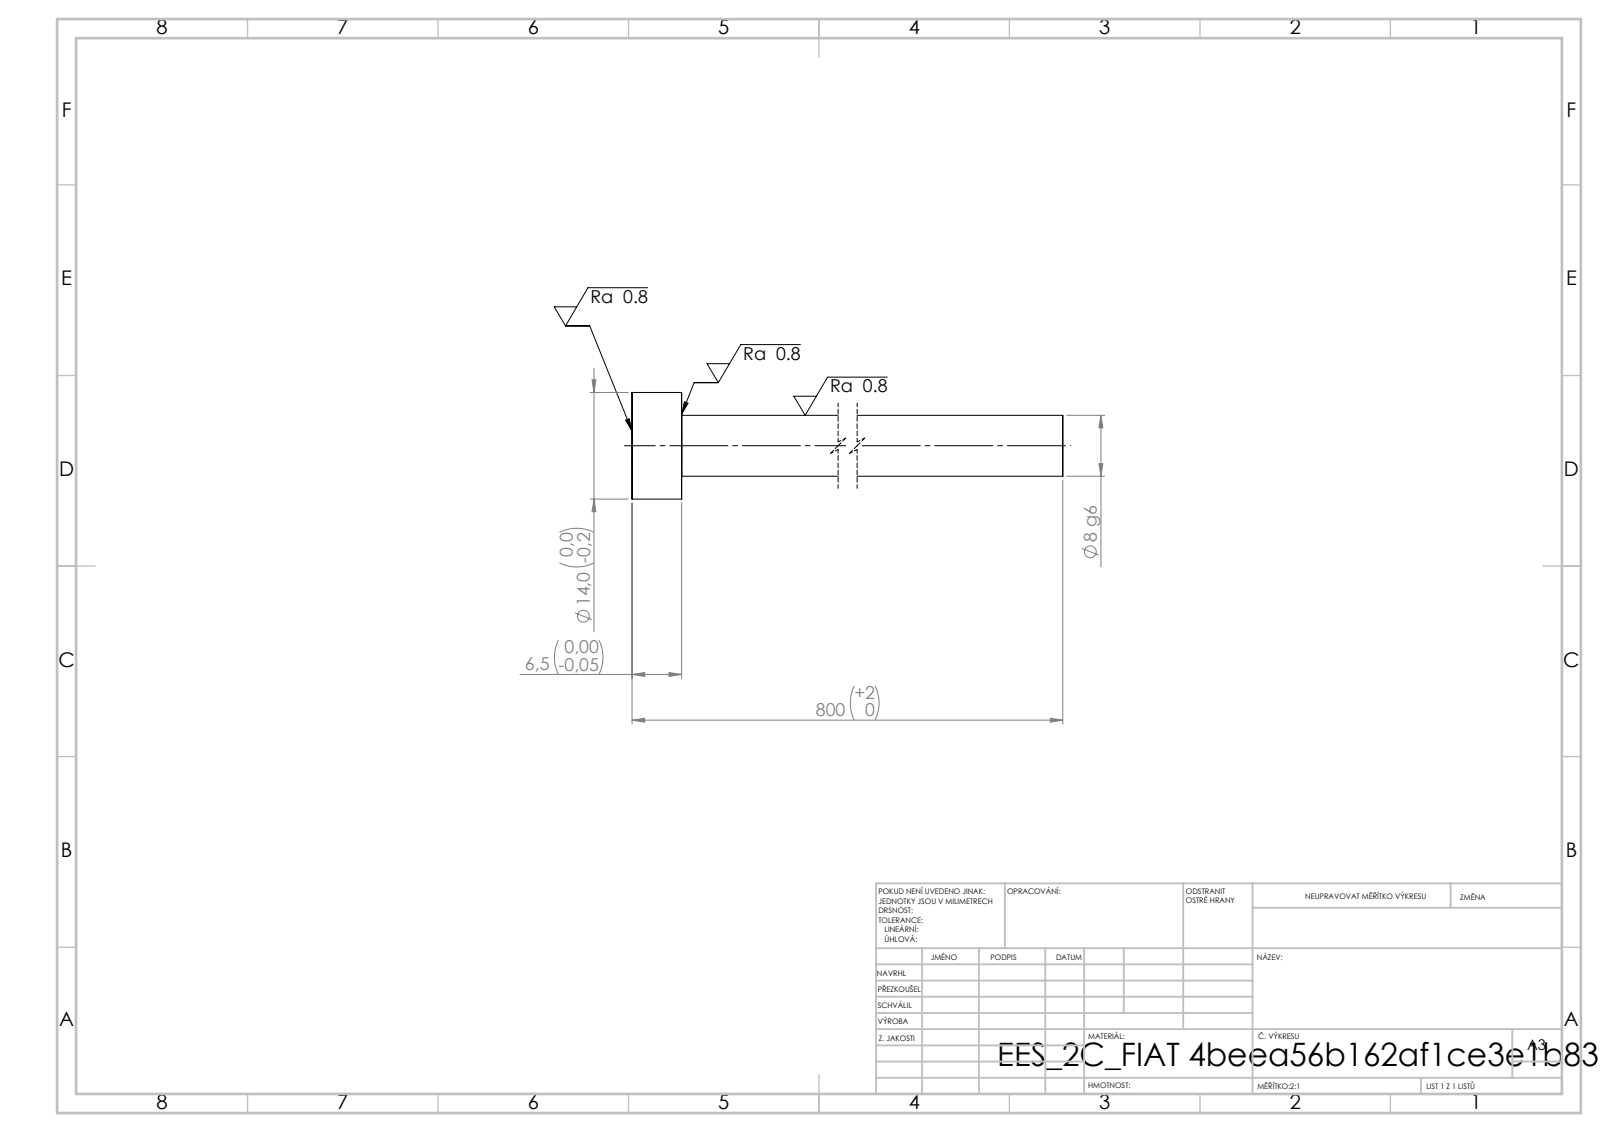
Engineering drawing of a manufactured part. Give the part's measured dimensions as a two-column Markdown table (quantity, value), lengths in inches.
| quantity | value |
| --- | --- |
| STEP written by | SolidWorks 2019 (CONFIG_CONTROL_DESIGN) |
| units | inches |
| bodies | 1 solid, 7 faces (3 planar, 4 cylindrical, 0 other) |
| overall size | 31.496 × 0.551 × 0.551 |
| volume | 2.495 in³ |
| surface area | 31.83 in² |
| round bosses / shafts (diameter × count) | 0.551 × 1, 0.315 × 1 |
| main face-to-face distances | 0.256, 31.496, 31.24 |
